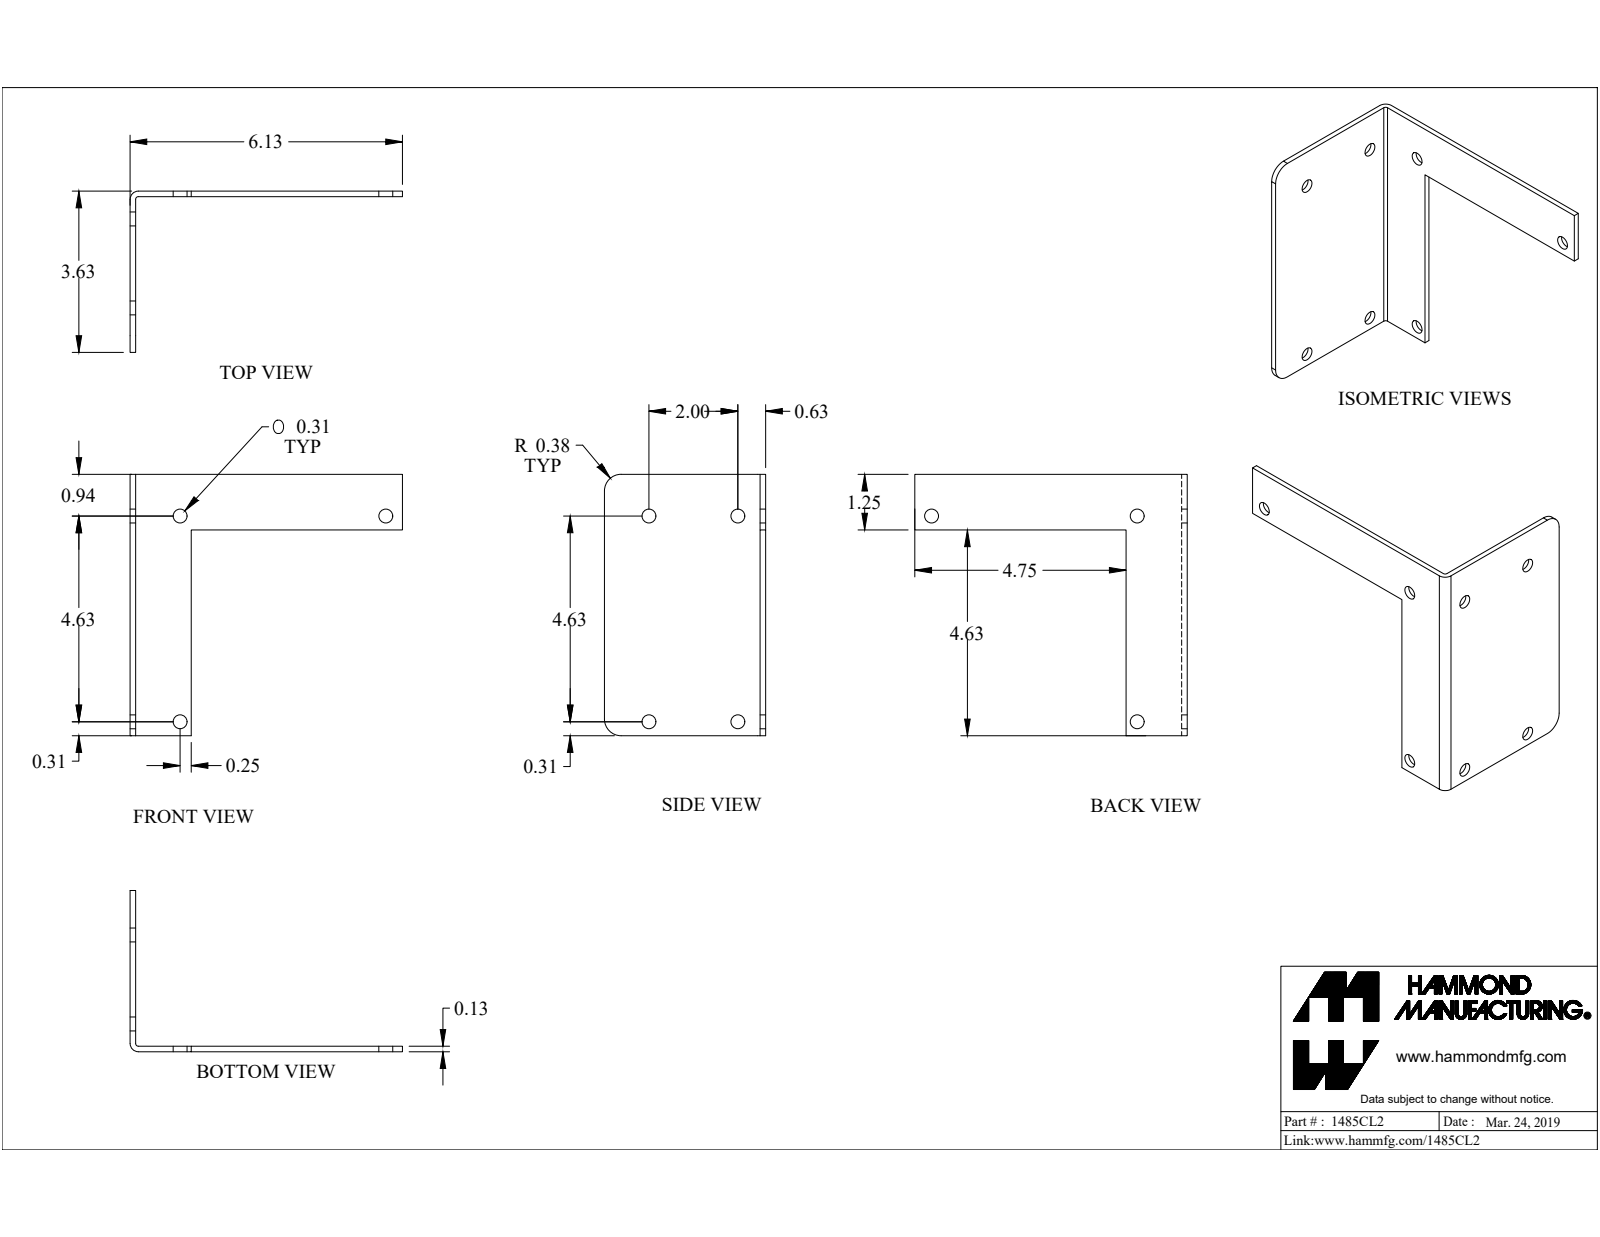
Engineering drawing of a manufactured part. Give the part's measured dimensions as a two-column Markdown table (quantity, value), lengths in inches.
| quantity | value |
| --- | --- |
| part name | 1485CL2 |
| STEP written by | SolidWorks 2019 (CONFIG_CONTROL_DESIGN) |
| units | inches |
| bodies | 1 solid, 21 faces (10 planar, 11 cylindrical, 0 other) |
| overall size | 6.125 × 5.875 × 3.625 |
| volume | 4.209 in³ |
| surface area | 72.02 in² |
| round holes (diameter × count) | 0.313 × 7 |
| partial cylindrical surfaces (radius × count) | 0.375 × 2, 0.06 × 1, 0.185 × 1 |
| main face-to-face distances | 0.125, 1.25, 3.5, 3.625, 1.375, 5.875, 4.625, 6.125, 6, 4.75 |
| hole center spacings | 4.625, 2, 5.039, 4.625, 6.541 |
